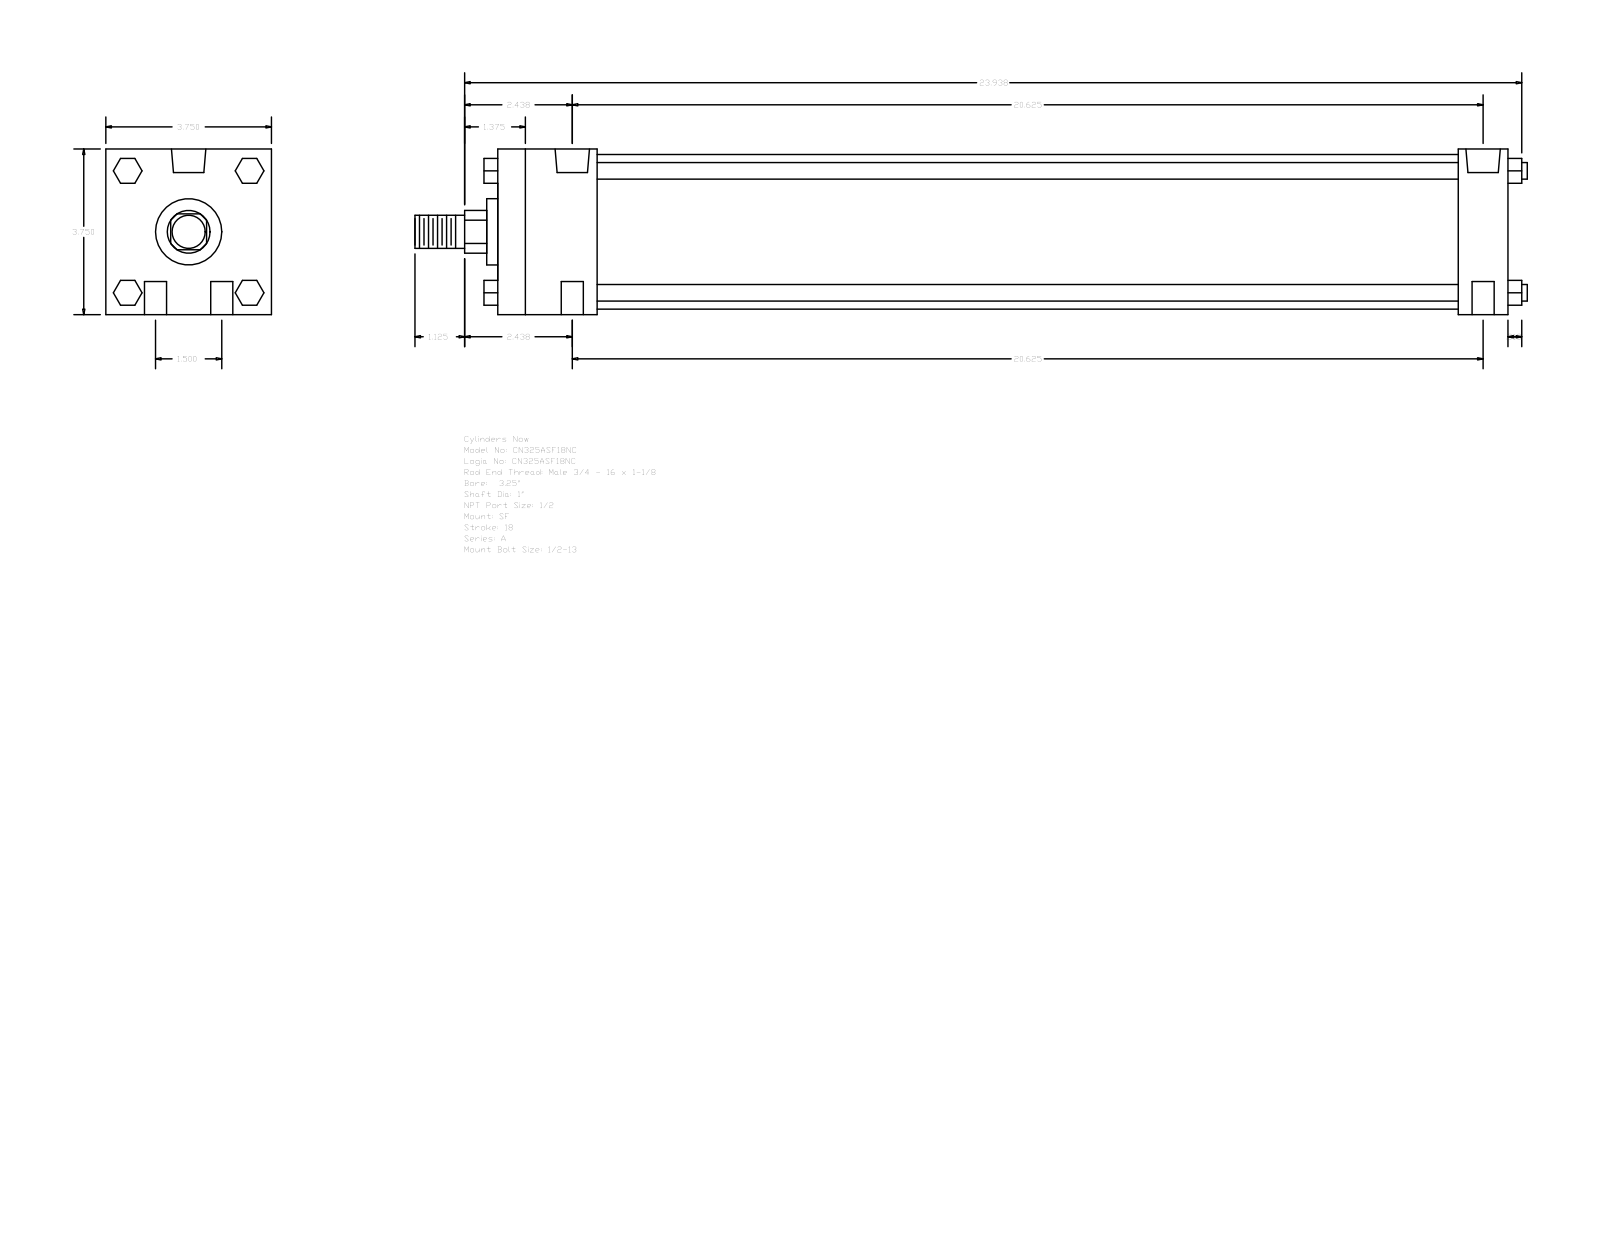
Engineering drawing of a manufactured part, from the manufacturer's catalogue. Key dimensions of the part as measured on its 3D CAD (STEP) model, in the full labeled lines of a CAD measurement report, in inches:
Part name (STEP PRODUCT): A_SF__0325_1
STEP written by: GSSL Pune (CONFIG_CONTROL_DESIGN)
Units: inches
Bodies: 0 solids, 124 faces (94 planar, 30 cylindrical, 0 other)
Overall size (bounding box): 25.187 × 3.75 × 3.75
Round holes (diameter × count): ⌀0.5 ×4, ⌀0.344 ×2, ⌀0.778 ×2
Round bosses / shafts (diameter × count): ⌀0.375 ×4, ⌀3.5 ×1, ⌀1.5 ×1, ⌀1 ×1, ⌀0.75 ×1
Partial cylindrical surfaces — rounded edges, fillets, slot ends (radius × count): R0.484 ×1
Main face-to-face distances: 3.75, 22.875, 21.75, 1.125, 2.25, 19.5, 20.625, 0.562, 1.38, 2.39
Hole centre spacings: 0.75, 20.639, 20.625, 1.5, 20.68, 20.375
